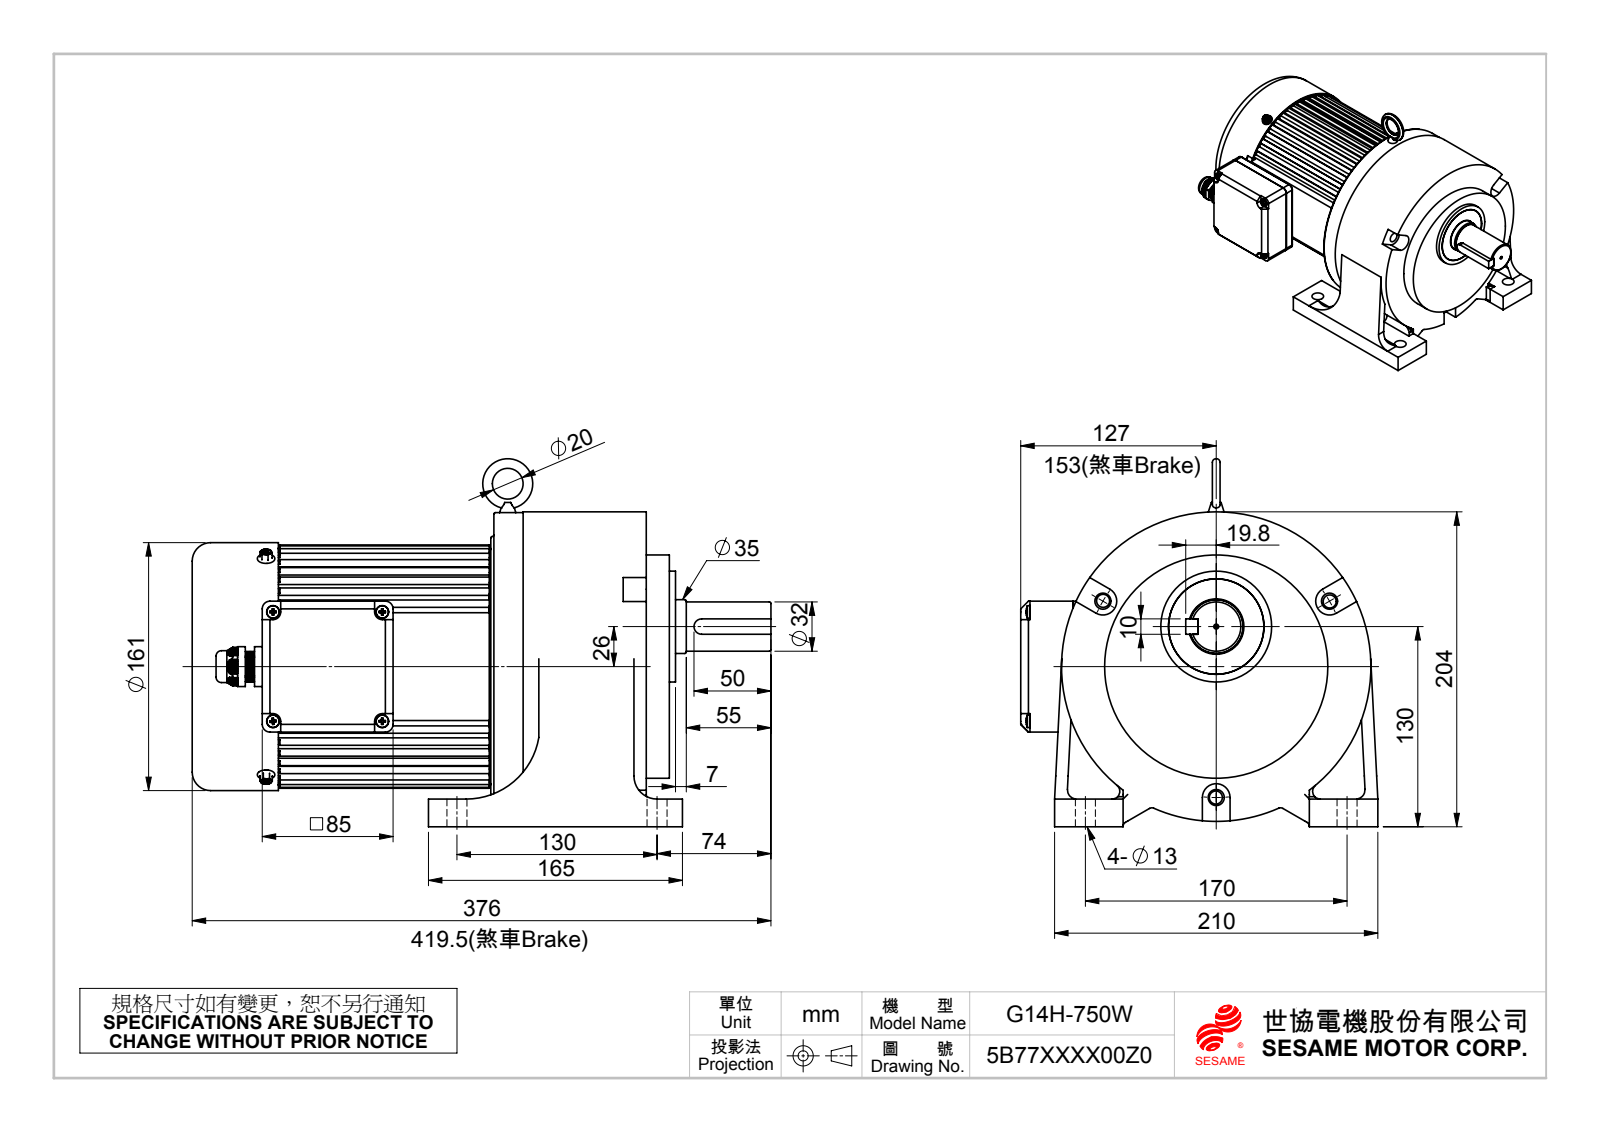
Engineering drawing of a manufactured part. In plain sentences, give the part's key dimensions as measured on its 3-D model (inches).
The part is named "出線盒上蓋; 油封35x62x8; G140S1; G14-750C2 (+8 more)". Its 3-D file was written by "SolidWorks 2010 (CONFIG_CONTROL_DESIGN)". It is 20 solids with 3047 faces: 1030 planar, 968 cylindrical and 1049 other. Overall it measures 14.803 by 9.409 by 9.134 inches. Its volume is 437.5 cubic inches and its surface area 1 026 square inches. Round holes: 11 of diameter 0.197, 9 of diameter 0.13, 5 of diameter 0.315, 4 of diameter 0.236, 4 of diameter 0.512, 3 of diameter 0.165, 3 of diameter 0.335, 3 of diameter 0.413, 3 of diameter 0.591, 1 of diameter 0.079, 1 of diameter 0.268, 1 of diameter 0.425. Round bosses or shafts: 4 of diameter 0.327, 4 of diameter 0.157, 3 of diameter 0.197, 1 of diameter 7.913, 1 of diameter 7.874, 1 of diameter 6.339, 1 of diameter 6.26, 1 of diameter 5.906. Partial cylindrical surfaces (rounded edges, fillets, slot ends): 75 of radius 0.079, 36 of radius 0.039, 11 of radius 0.197, 10 of radius 0.118, 7 of radius 0.315, 6 of radius 0.02, 6 of radius 0.098, 5 of radius 0.394. The main face-to-face distances are 0.079, 0.709, 1.063, 5.512, 6.575, 0.472, 5.807, 0.374, 5.886, 6.949. The hole center spacings are 3.346, 5.796, 1.772, 2.55, 2.795, 5.791, 0.433, 0.453.
